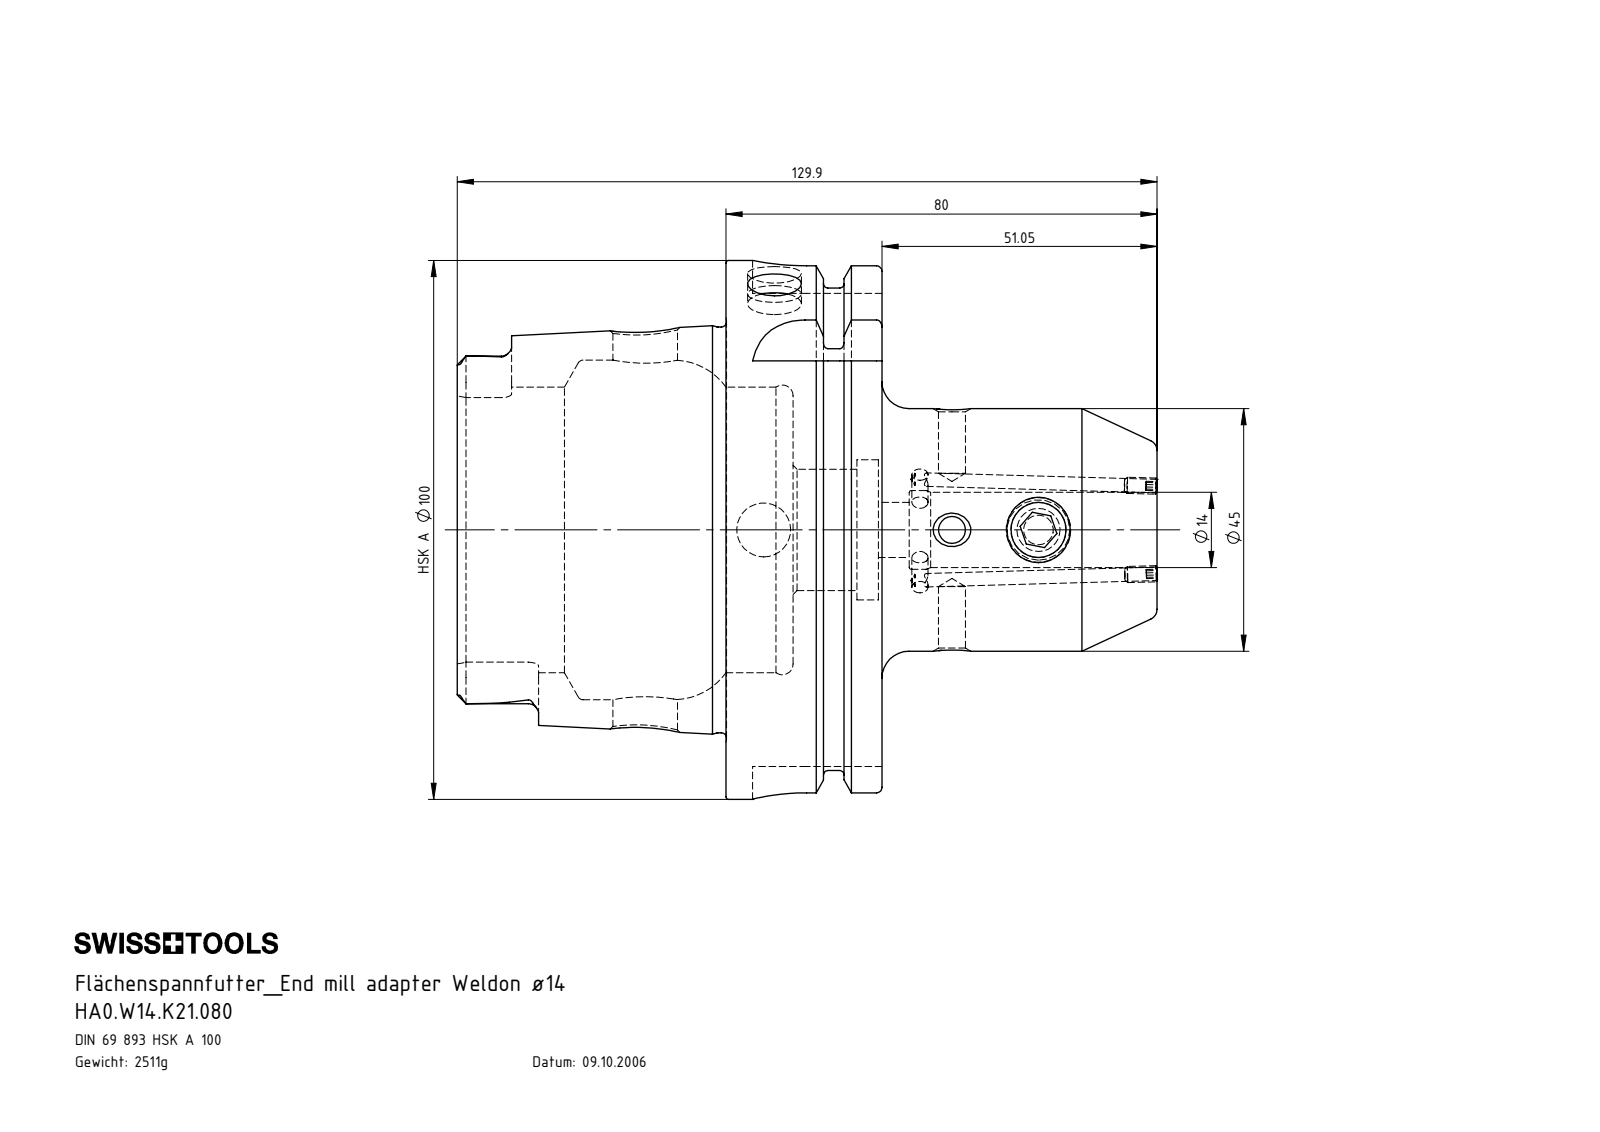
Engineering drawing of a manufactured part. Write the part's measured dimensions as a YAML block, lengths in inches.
part_name: "HA0.W14.K21.080; ERU-CJ2.001.006; W12-ER1.001.016; HA0-W14.K21.080_C_Fertigbearbeitung"
step_written_by: "SolidWorks 2012 (CONFIG_CONTROL_DESIGN)"
units: inches
bodies: {solids: 4, faces: 271, planar: 71, cylindrical: 82, other: 118}
overall_size: [5.117, 3.937, 3.937]
volume: 19.52
surface_area: 94.47
round_holes:
  - {diameter: 0.394, count: 3}
  - {diameter: 0.098, count: 2}
  - {diameter: 0.197, count: 2}
  - {diameter: 0.404, count: 2}
  - {diameter: 0.118, count: 1}
  - {diameter: 0.472, count: 1}
  - {diameter: 0.551, count: 1}
  - {diameter: 0.575, count: 1}
  - {diameter: 0.886, count: 1}
  - {diameter: 1.024, count: 1}
  - {diameter: 2.087, count: 1}
  - {diameter: 2.48, count: 1}
round_bosses_or_shafts:
  - {diameter: 0.118, count: 2}
  - {diameter: 3.937, count: 1}
  - {diameter: 3.62, count: 1}
  - {diameter: 2.963, count: 1}
  - {diameter: 1.772, count: 1}
  - {diameter: 0.472, count: 1}
partial_cylinders:
  - {radius: 0.075, count: 6}
  - {radius: 0.192, count: 4}
  - {radius: 0.394, count: 4}
face_to_face_distances: [1.14, 0.65, 0.49, 1.965, 2.455, 3.104, 5.114, 3.15, 2.659, 2.01]
hole_center_spacings: [0.632, 1.376, 2.008, 2.242]
